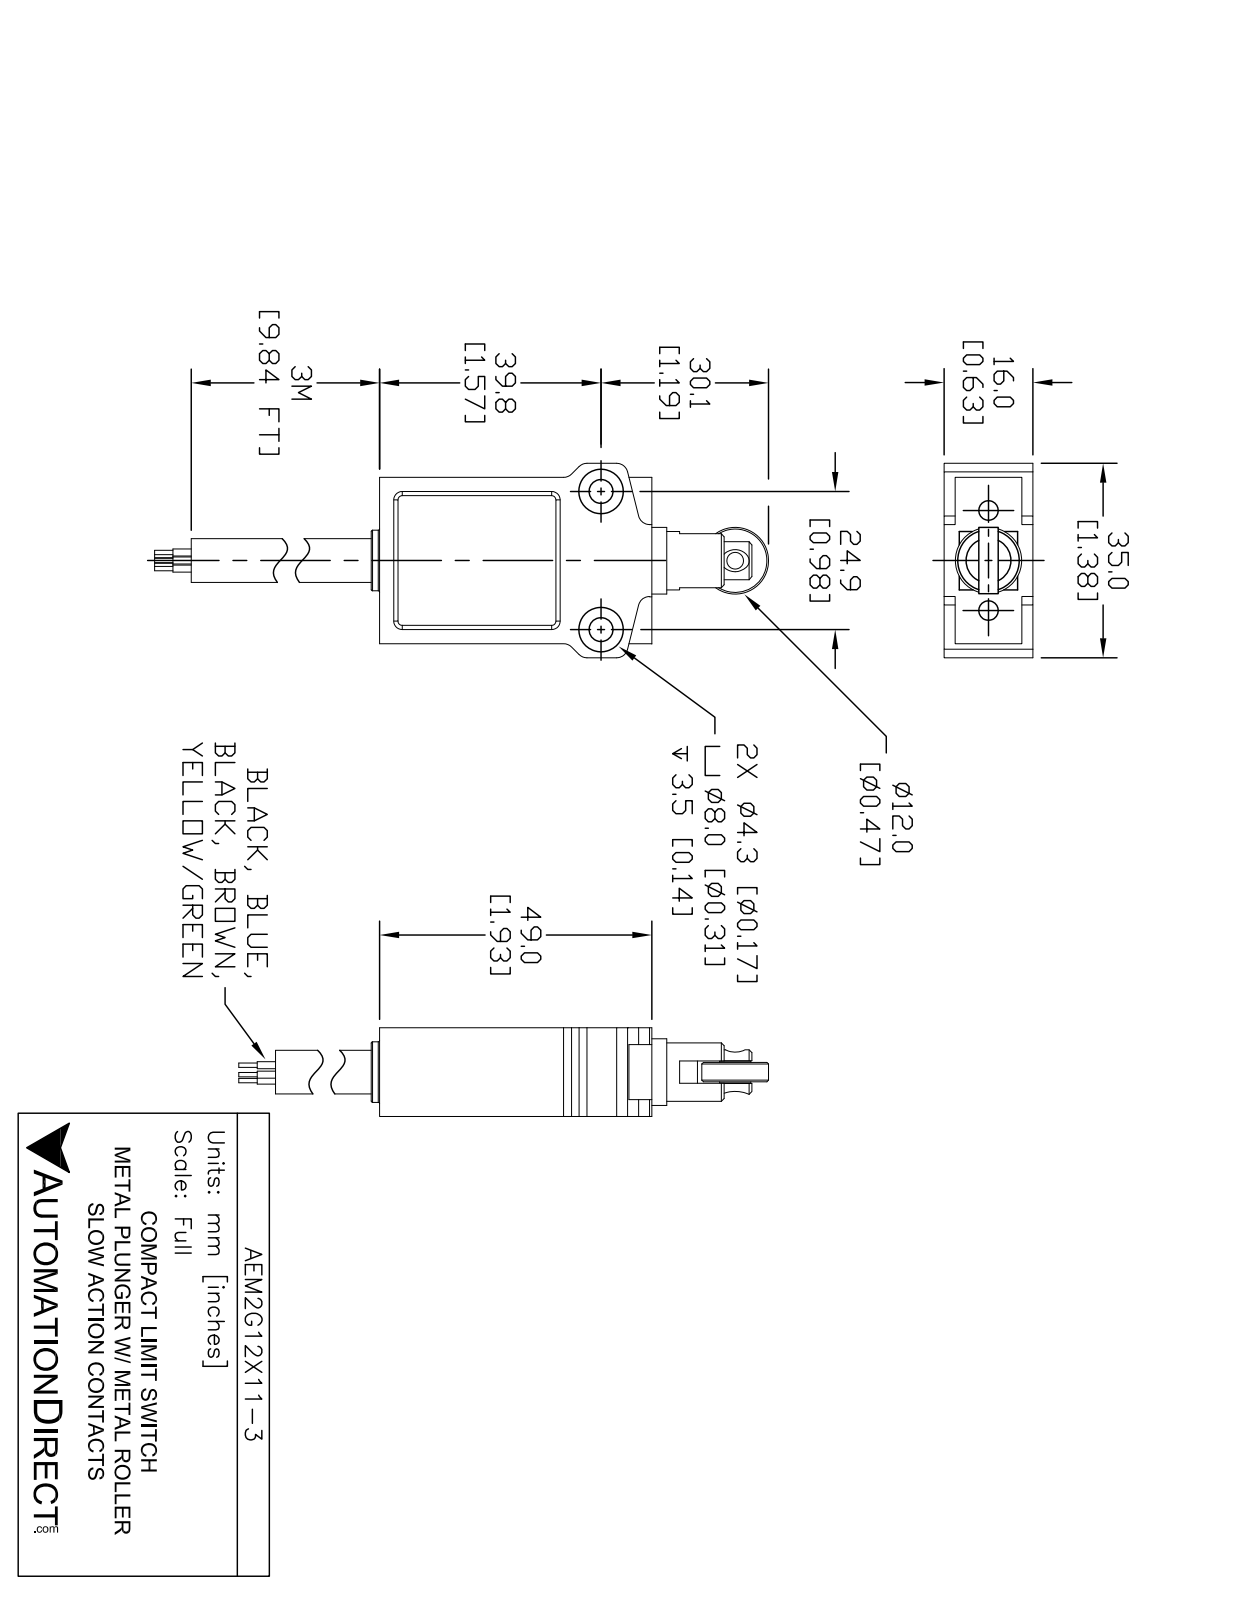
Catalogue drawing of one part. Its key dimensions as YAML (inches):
part_name: "AEM2G12X11-3_Default"
step_written_by: "SolidWorks 2021 (CONFIG_CONTROL_DESIGN)"
units: inches
bodies: {solids: 2, faces: 116, planar: 53, cylindrical: 43, other: 20}
overall_size: [3.375, 1.38, 0.63]
volume: 1.427
surface_area: 11.97
round_holes:
  - {diameter: 0.138, count: 2}
  - {diameter: 0.177, count: 2}
  - {diameter: 0.344, count: 2}
round_bosses_or_shafts:
  - {diameter: 0.05, count: 5}
  - {diameter: 0.031, count: 5}
  - {diameter: 0.47, count: 2}
  - {diameter: 0.43, count: 1}
  - {diameter: 0.41, count: 1}
  - {diameter: 0.31, count: 1}
partial_cylinders:
  - {radius: 0.03, count: 8}
  - {radius: 0.08, count: 8}
  - {radius: 0.135, count: 1}
face_to_face_distances: [0.03, 0.6, 0.57, 0.63, 1.18, 1.93, 0.235, 0.395, 0.205, 0.365]
hole_center_spacings: [0.7, 0.98]
